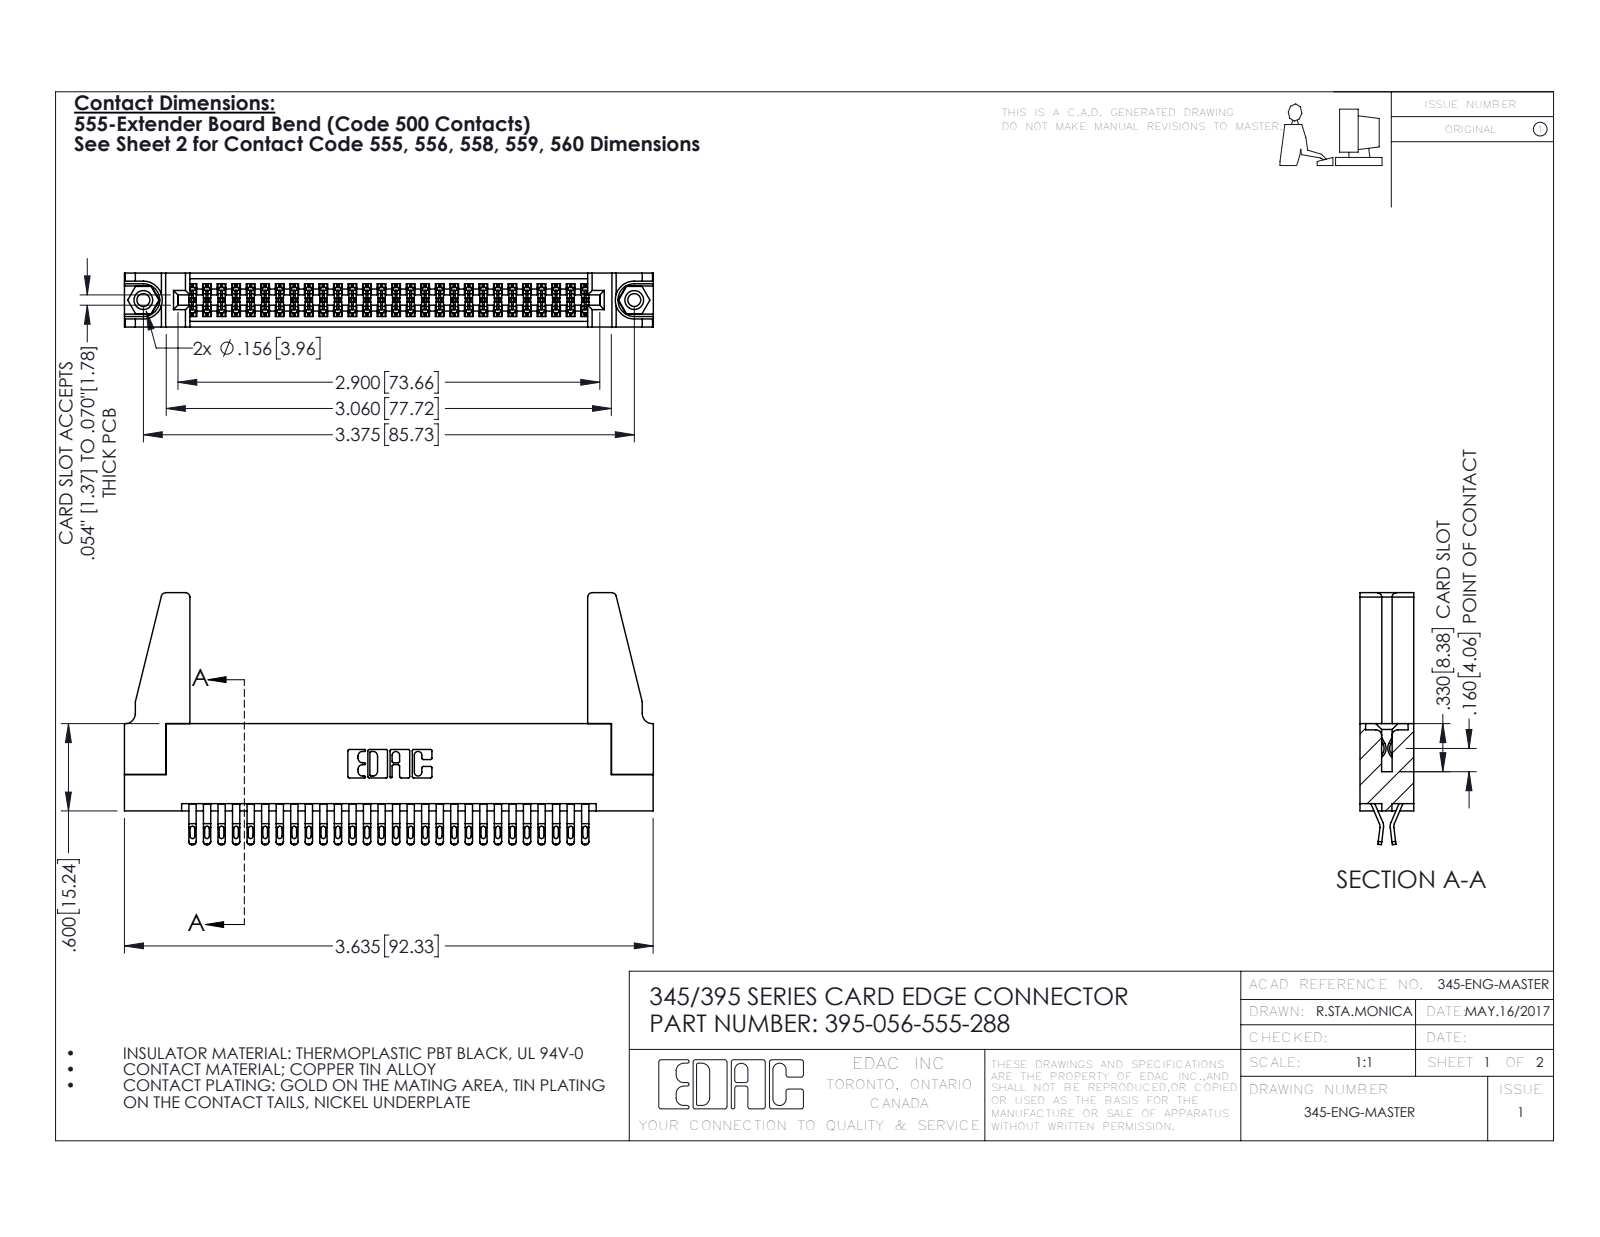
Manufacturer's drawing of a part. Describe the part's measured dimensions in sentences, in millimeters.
The part is named "345 Part_Flush Mounting Lugs - 0.156 Dia-TH; 345-250-001_345-250-001-102; 345-292-001_555 Tail; 345-220-078_345-220-088 (+1 more)". Its 3-D file was written by "SolidWorks 2016 (CONFIG_CONTROL_DESIGN)". It is 61 solids with 3386 faces: 1888 planar, 1482 cylindrical and 16 other. Overall it measures 92.4 by 44 by 9.4 millimeters. Its volume is 12 300 cubic millimeters and its surface area 16 720 square millimeters. Round holes: 2 of diameter 2.3, 2 of diameter 3.2, 2 of diameter 4, 1 of diameter 1.6. Round bosses or shafts: 2 of diameter 3.9. Partial cylindrical surfaces (rounded edges, fillets, slot ends): 140 of radius 0.4, 112 of radius 0.5, 84 of radius 0.2, 22 of radius 0.3, 8 of radius 0.8, 6 of radius 0.2, 6 of radius 0.8, 3 of radius 0.7. The main face-to-face distances are 1.8, 7.6, 9.4, 5.1, 0.6, 2.5, 6.9, 5.7, 4.4, 3.8. The hole center spacings are 6.9, 79.8, 85.7.
